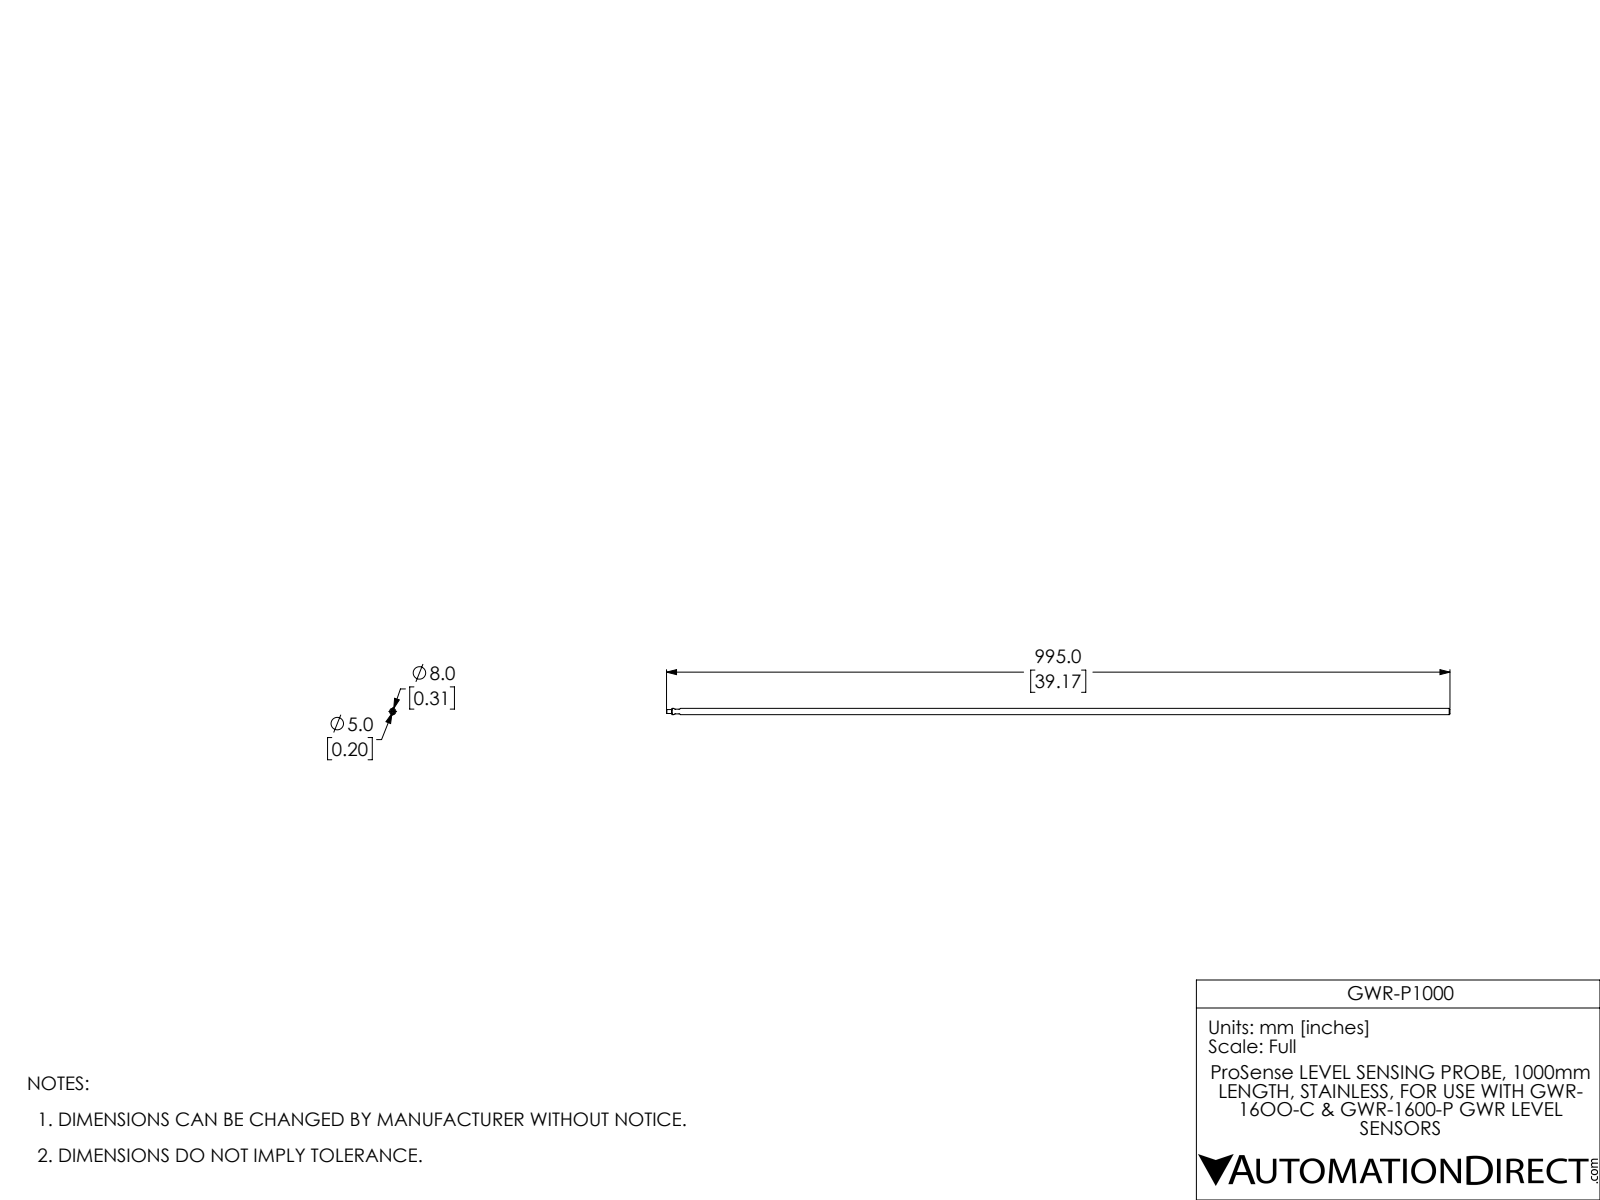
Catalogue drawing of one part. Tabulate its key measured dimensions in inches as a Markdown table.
| quantity | value |
| --- | --- |
| part name | GWR-P1000 |
| STEP written by | SolidWorks 2017 (AUTOMOTIVE_DESIGN) |
| units | inches |
| bodies | 1 solid, 19 faces (5 planar, 8 cylindrical, 6 other) |
| overall size | 39.173 × 0.315 × 0.315 |
| volume | 3.035 in³ |
| surface area | 38.79 in² |
| round bosses / shafts (diameter × count) | 0.315 × 1, 0.197 × 1 |
| partial cylindrical surfaces (radius × count) | 0.079 × 4 |
| main face-to-face distances | 38.898, 0.236, 39.173, 0.276 |
